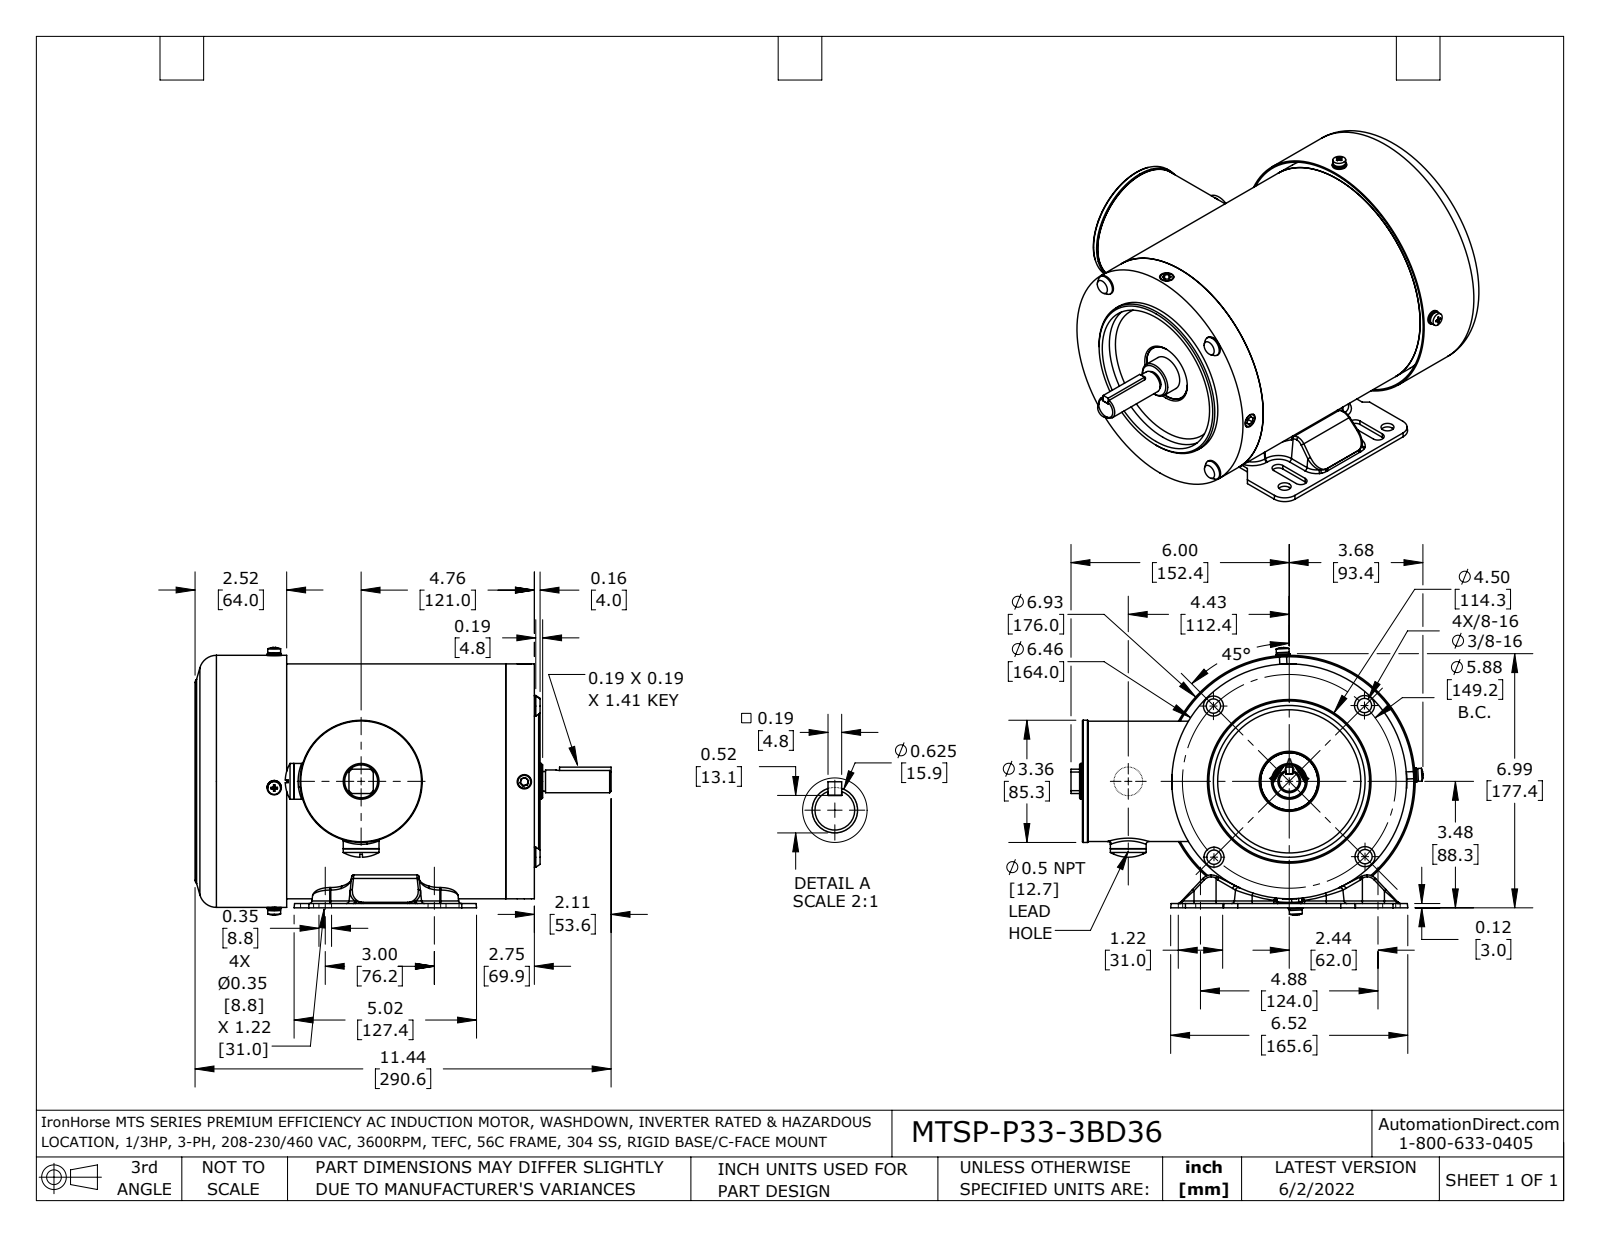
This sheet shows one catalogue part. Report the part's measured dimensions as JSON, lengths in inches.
{"part_name": "MTSP-P33-3BD36", "step_written_by": "SolidWorks 2021 (AUTOMOTIVE_DESIGN)", "units": "inches", "bodies": {"solids": 40, "faces": 1660, "planar": 442, "cylindrical": 579, "other": 639}, "overall_size": [11.441, 9.68, 7.357], "volume_in3": 54.38, "surface_area_in2": 932, "round_holes": [[0.165, 10], [0.217, 8], [0.213, 4], [0.236, 4], [0.256, 4], [0.335, 4], [0.354, 4], [0.358, 4], [0.118, 2], [0.472, 2], [0.656, 2], [1.378, 2]], "round_bosses_or_shafts": [[0.394, 8], [0.551, 4], [0.354, 4], [0.331, 4], [0.315, 4], [0.197, 4], [0.984, 3], [0.787, 2]], "partial_cylinders_radius": [[0.079, 58], [0.039, 39], [0.128, 36], [0.012, 16], [0.118, 14], [0.173, 8], [0.236, 8], [0.059, 6]], "face_to_face_distances": [0.118, 7.323, 0.236, 0.039, 7.087, 7.205, 7.441, 1.949, 1.831, 9.272], "hole_center_spacings": [2.937, 4.154, 0.133, 1.181, 1.312, 1.917, 2.992, 3.163]}
